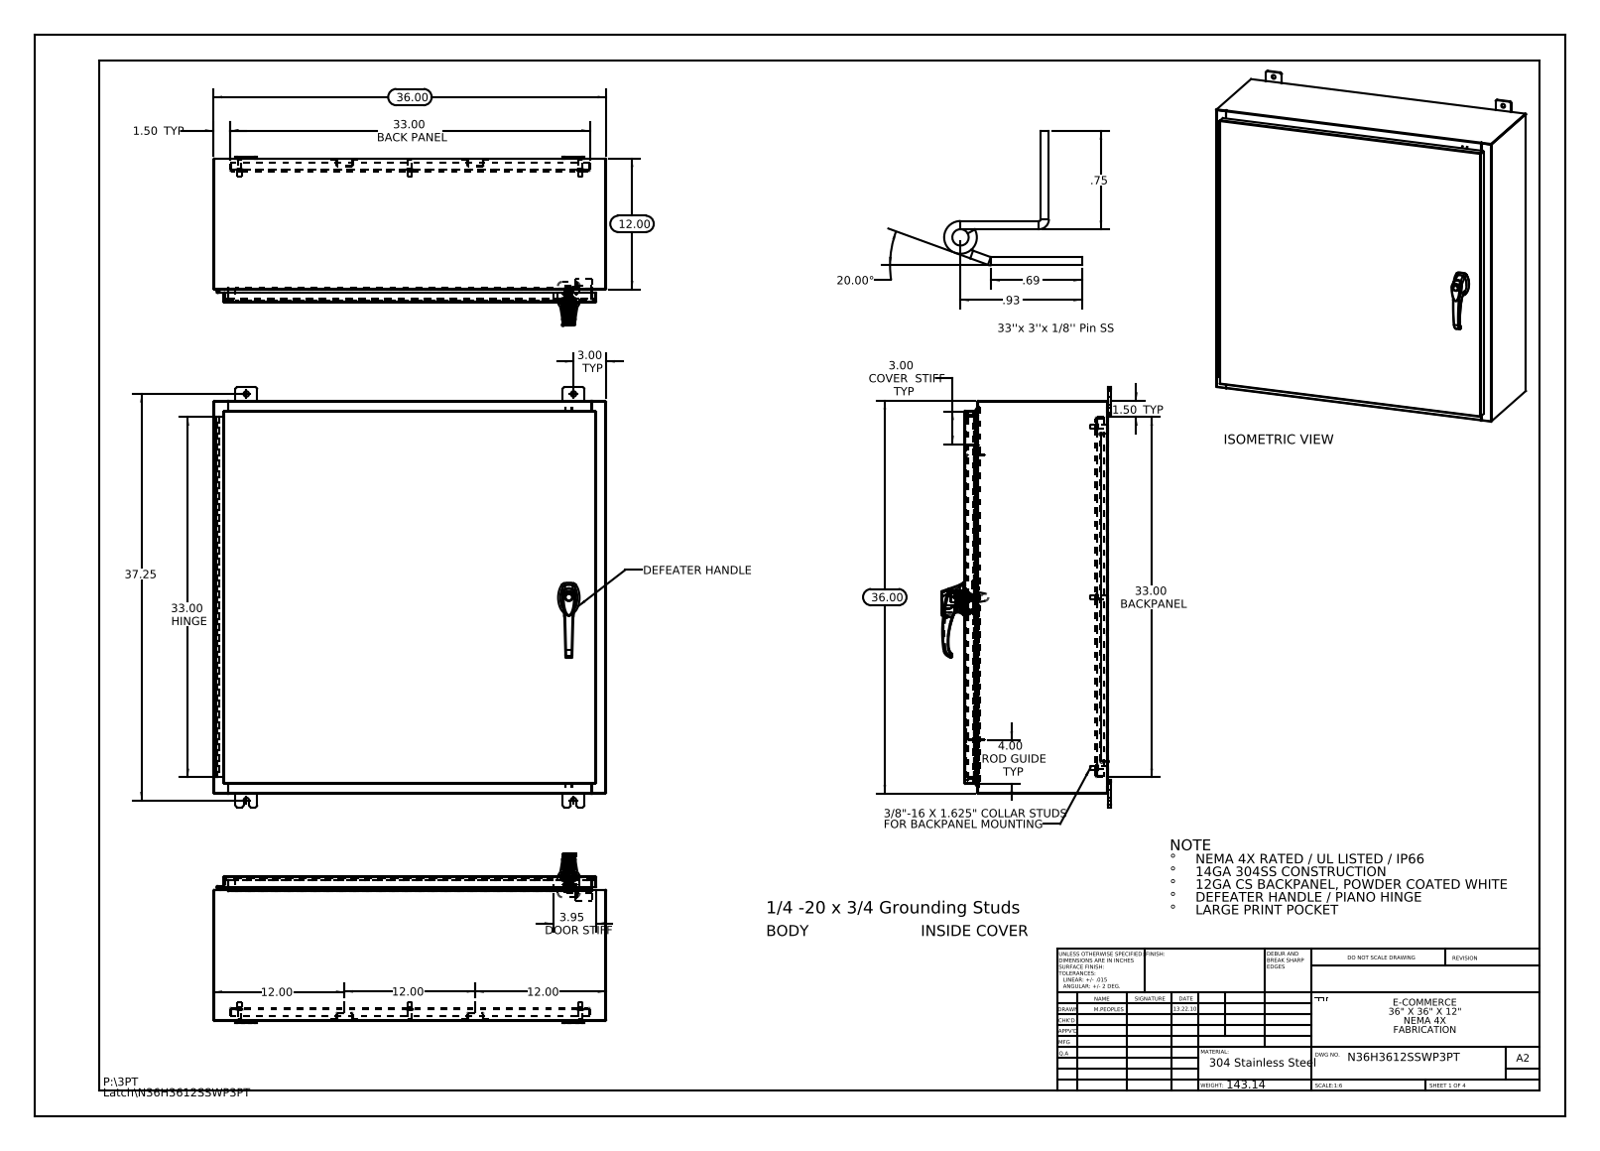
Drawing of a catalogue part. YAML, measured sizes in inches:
part_name: "012103_012102; 2616310101; N36H3612SSWP3PT Bottom; N36H3612SSWP3PT Defeater Handle Rod (+8 more)"
step_written_by: "SolidWorks 2013 (CONFIG_CONTROL_DESIGN)"
units: inches
bodies: {solids: 39, faces: 2936, planar: 1129, cylindrical: 1113, other: 694}
overall_size: [38.5, 36, 15.495]
volume: 513.7
surface_area: 12791
round_holes:
  - {diameter: 0.5, count: 12}
  - {diameter: 0.25, count: 10}
  - {diameter: 0.138, count: 3}
  - {diameter: 0.161, count: 3}
  - {diameter: 0.079, count: 2}
  - {diameter: 0.203, count: 2}
  - {diameter: 0.313, count: 2}
  - {diameter: 0.437, count: 2}
  - {diameter: 0.125, count: 1}
  - {diameter: 0.125, count: 1}
  - {diameter: 0.197, count: 1}
  - {diameter: 0.276, count: 1}
round_bosses_or_shafts:
  - {diameter: 0.625, count: 8}
  - {diameter: 0.375, count: 8}
  - {diameter: 0.33, count: 8}
  - {diameter: 1.181, count: 1}
  - {diameter: 0.748, count: 1}
  - {diameter: 0.68, count: 1}
  - {diameter: 0.661, count: 1}
  - {diameter: 0.639, count: 1}
partial_cylinders:
  - {radius: 0.118, count: 37}
  - {radius: 0.013, count: 34}
  - {radius: 0.006, count: 33}
  - {radius: 0.088, count: 28}
  - {radius: 0.19, count: 24}
  - {radius: 0.039, count: 15}
  - {radius: 0.028, count: 12}
  - {radius: 0.008, count: 6}
face_to_face_distances: [0.075, 13.126, 35.925, 13.051, 13.201, 0.104, 1, 12.126, 1.075, 12.051]
hole_center_spacings: [15.625, 11.363, 13.669, 22.097, 34.939, 34.939, 31.25, 31.25]
